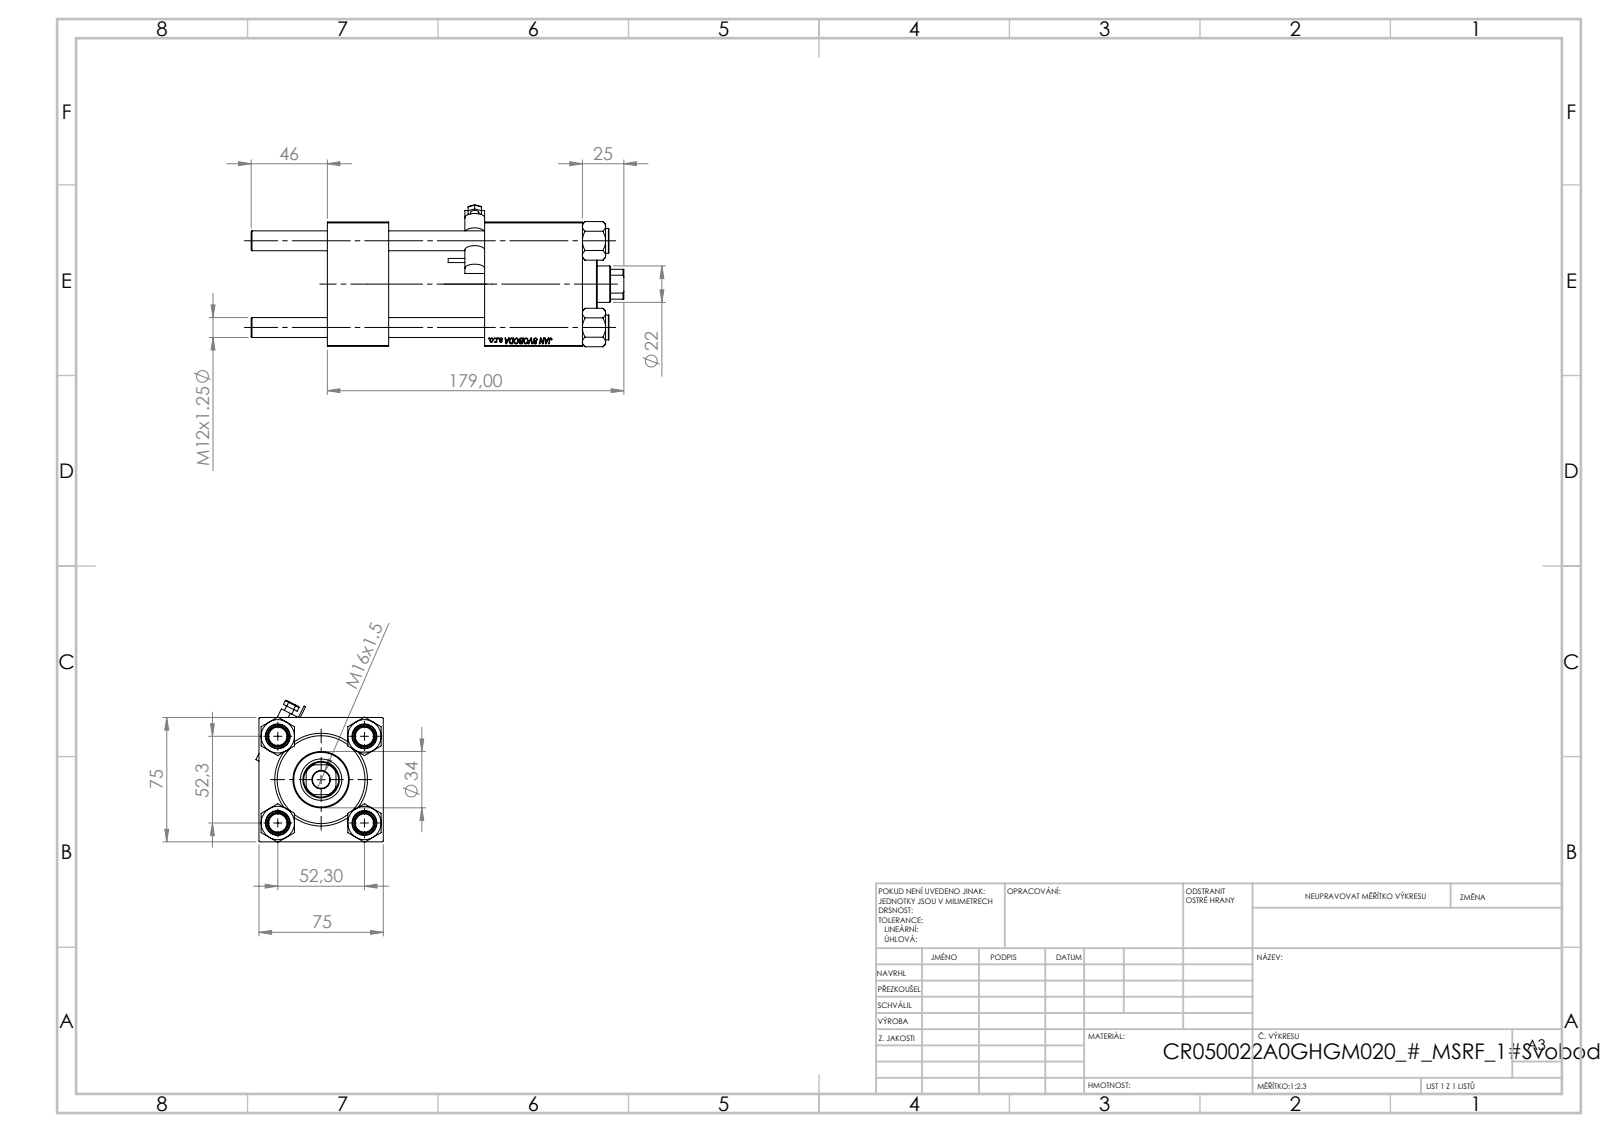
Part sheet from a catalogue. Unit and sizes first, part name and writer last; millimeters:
Units: millimetres
Overall size (bounding box): 225 × 85.68 × 76.88
Round holes (diameter × count): ⌀12 ×4, ⌀7 ×2, ⌀20.96 ×2, ⌀30 ×2, ⌀10.5 ×1, ⌀22 ×1, ⌀25 ×1, ⌀41 ×1, ⌀50 ×1, ⌀53 ×1
Round bosses / shafts (diameter × count): ⌀15 ×4, ⌀56 ×1, ⌀34 ×1, ⌀5 ×1, ⌀2.5 ×1
Partial cylindrical surfaces — rounded edges, fillets, slot ends (radius × count): R0.5 ×6, R6 ×2, R10.5 ×1
Main face-to-face distances: 75, 37, 154, 117, 95, 58, 59, 125.3, 88.3, 30.3
Hole centre spacings: 36.98, 52.3, 73.96, 93.5
Volume: 693 777 mm³ · Surface area: 165 989 mm²
Bodies: 12 solids, 1166 faces (538 planar, 92 cylindrical, 536 other)
Part name (STEP PRODUCT): CR025_012_A_0_G_A_G_M_020_+#_##_TYCINKA; V215CR_BODY_A; V215_VC_A; V215CR_VCP (+2 more)
STEP written by: SolidWorks 2019 (CONFIG_CONTROL_DESIGN)
